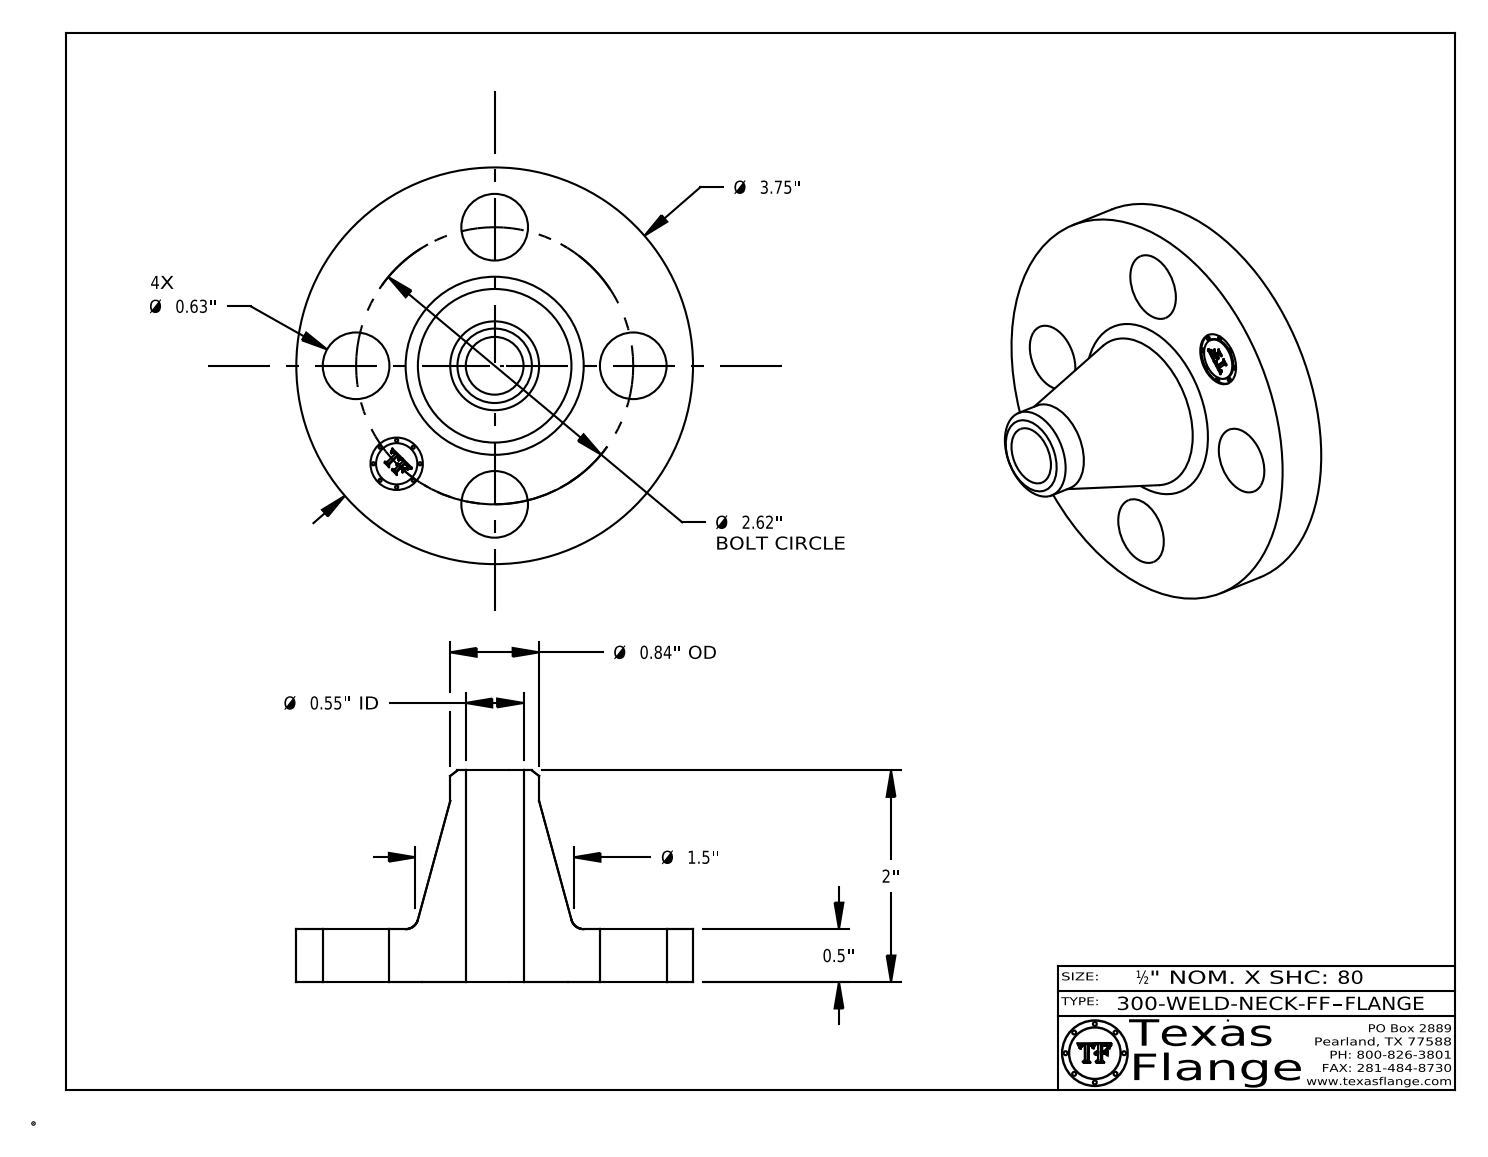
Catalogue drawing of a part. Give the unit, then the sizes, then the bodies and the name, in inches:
Units: inches
Overall size (bounding box): 3.75 × 3.75 × 2
Round holes (diameter × count): ⌀0.63 ×4, ⌀0.495 ×1, ⌀0.546 ×1
Round bosses / shafts (diameter × count): ⌀0.03 ×8, ⌀3.75 ×1, ⌀0.84 ×1, ⌀0.39 ×1
Main face-to-face distances: 0.5, 2, 1.5, 0.485, 0.015, 1.515, 0.148, 0.144, 0.027, 0.096
Hole centre spacings: 1.31, 1.852, 1.003, 2.42, 2.62, 1.31
Volume: 5.93 in³ · Surface area: 36.45 in²
Bodies: 1 solid, 409 faces (369 planar, 34 cylindrical, 6 other)
Part name (STEP PRODUCT): 300-WELD-NECK-FF
STEP written by: CATIA V5 STEP AP214 (AUTOMOTIVE_DESIGN)
